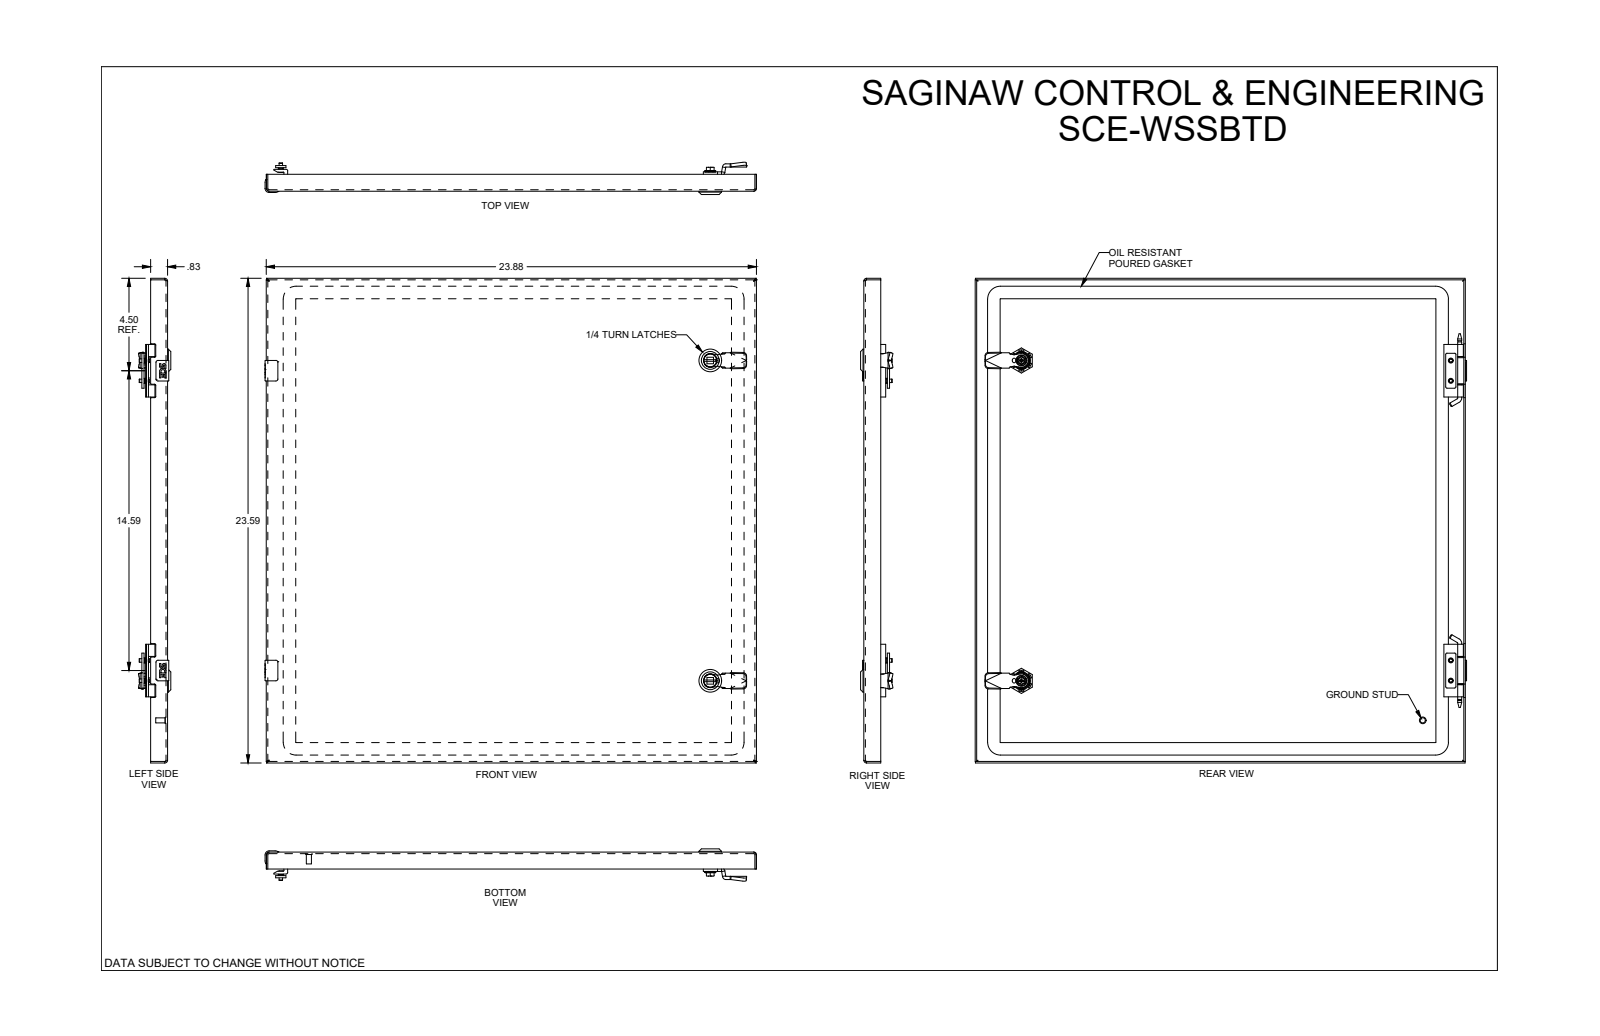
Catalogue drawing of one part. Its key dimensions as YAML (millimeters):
part_name: "SCE-WSSBTD"
step_written_by: "SolidWorks 2021 (AUTOMOTIVE_DESIGN)"
units: millimeters
bodies: {solids: 31, faces: 1513, planar: 754, cylindrical: 523, other: 236}
overall_size: [607.9, 599.3, 40]
volume: 1063000
surface_area: 963200
round_holes:
  - {diameter: 4.4, count: 4}
  - {diameter: 5.2, count: 4}
  - {diameter: 6.2, count: 4}
  - {diameter: 9.5, count: 4}
  - {diameter: 5, count: 2}
  - {diameter: 5.5, count: 2}
  - {diameter: 8, count: 2}
  - {diameter: 10, count: 2}
  - {diameter: 16.1, count: 2}
  - {diameter: 20.4, count: 2}
  - {diameter: 5.2, count: 1}
  - {diameter: 5.2, count: 1}
round_bosses_or_shafts:
  - {diameter: 4.3, count: 6}
  - {diameter: 6.4, count: 4}
  - {diameter: 5, count: 3}
  - {diameter: 28, count: 2}
  - {diameter: 19.8, count: 2}
  - {diameter: 16, count: 2}
  - {diameter: 13.5, count: 2}
  - {diameter: 12.8, count: 2}
partial_cylinders:
  - {radius: 0.3, count: 56}
  - {radius: 0.4, count: 24}
  - {radius: 0.5, count: 20}
  - {radius: 1.6, count: 8}
  - {radius: 2.5, count: 8}
  - {radius: 4, count: 8}
  - {radius: 5.6, count: 8}
  - {radius: 1.7, count: 6}
face_to_face_distances: [1.9, 597.4, 604.5, 595.5, 602.6, 599.3, 606.4, 7.1, 9, 19.1]
hole_center_spacings: [531.9, 370.7, 25, 25, 345.7, 370.7, 531.3, 647.9]
